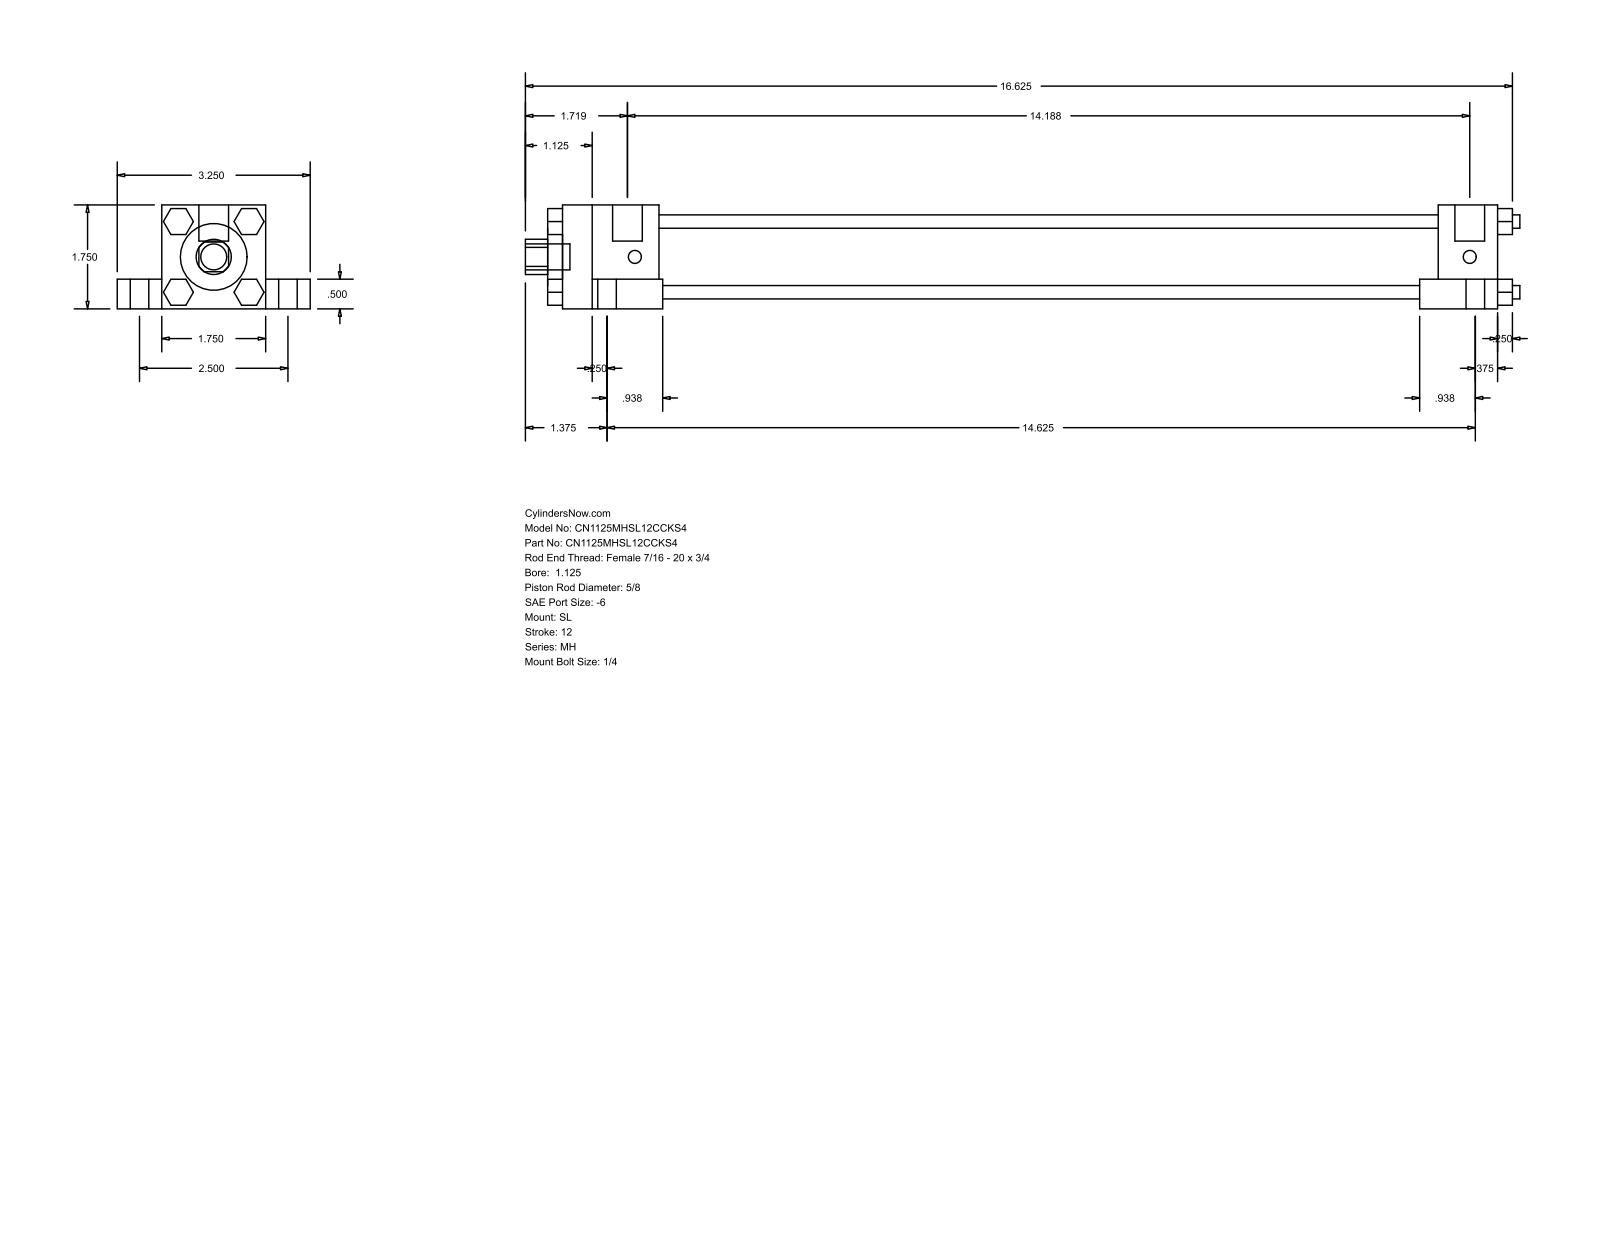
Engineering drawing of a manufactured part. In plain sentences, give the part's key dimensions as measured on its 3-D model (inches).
The part is named "MH_SL__0112_0.625". Its 3-D file was written by "GSSL Pune (CONFIG_CONTROL_DESIGN)". It is 0 solids with 150 faces: 114 planar, 36 cylindrical and 0 other. Overall it measures 16.75 by 3.25 by 1.75 inches. Round holes: 1 of diameter 0.625, 1 of diameter 1.125, 1 of diameter 1.375. Round bosses or shafts: 4 of diameter 0.563, 4 of diameter 0.313, 4 of diameter 0.225, 4 of diameter 0.219, 2 of diameter 0.5, 1 of diameter 0.437. Partial cylindrical surfaces (rounded edges, fillets, slot ends): 1 of radius 0.297. The main face-to-face distances are 1.75, 0.75, 0.5, 1.25, 2.5, 0.437, 1.313, 13.938, 13.125, 14.125.
